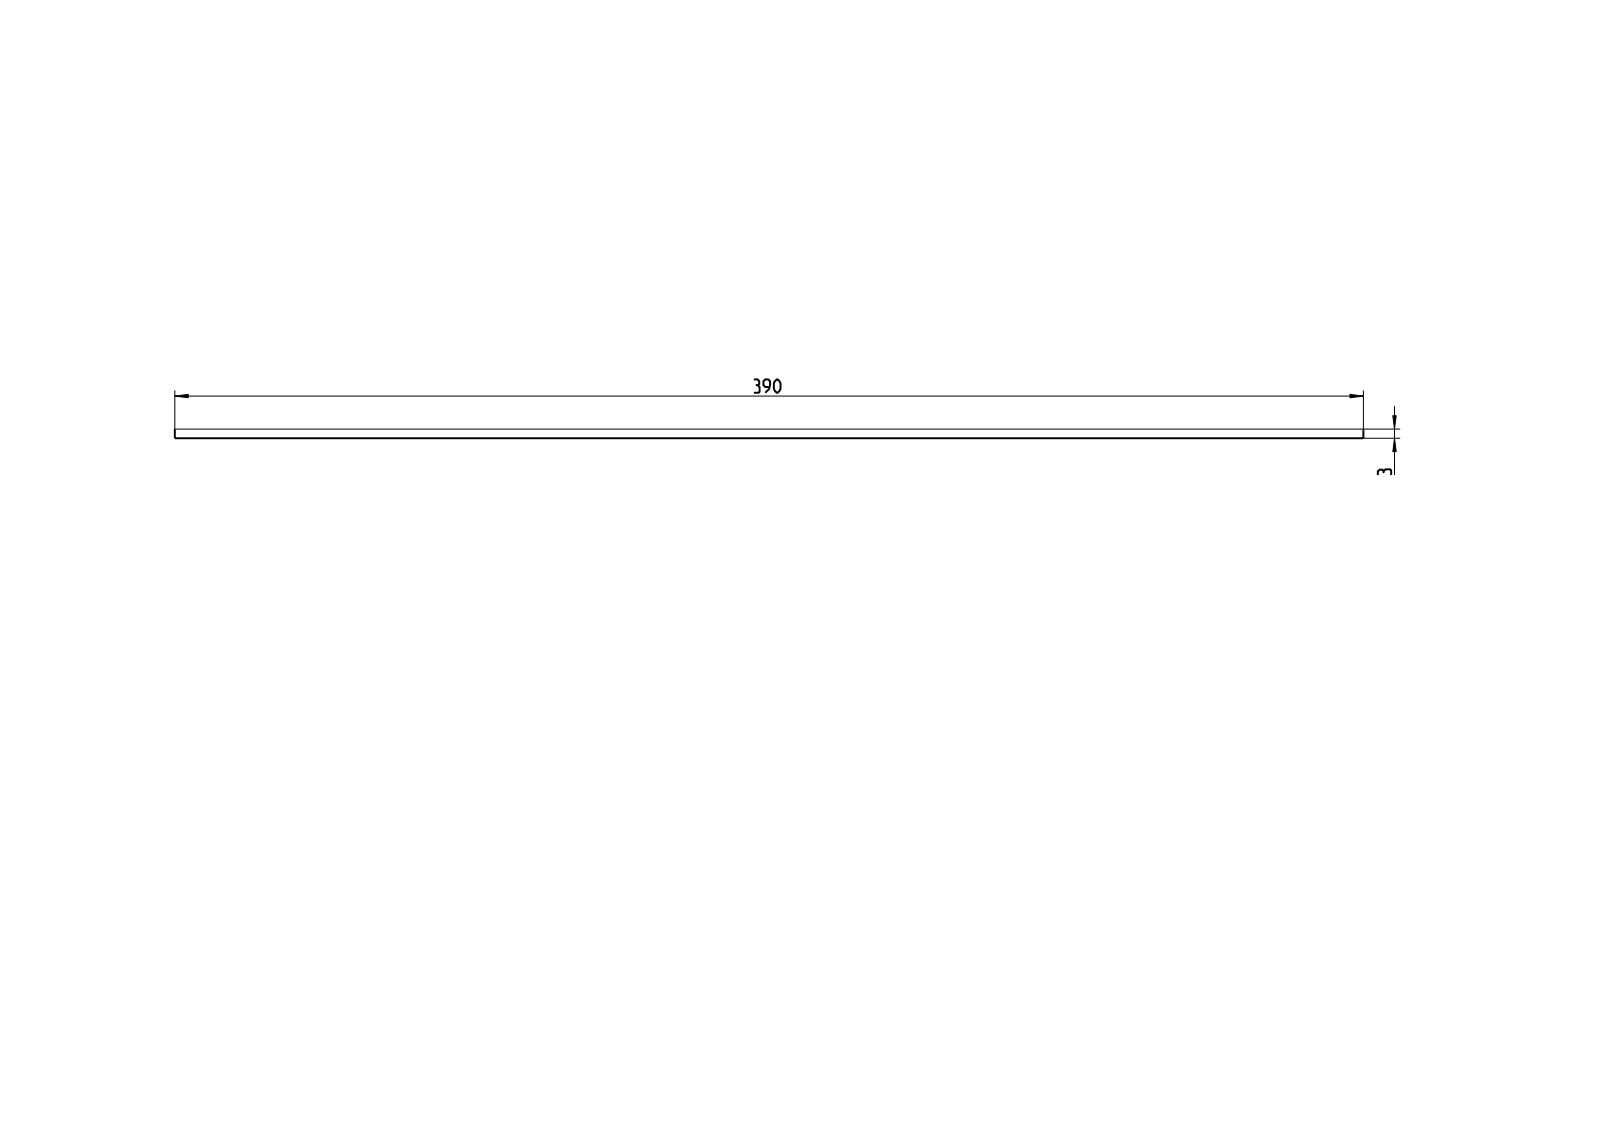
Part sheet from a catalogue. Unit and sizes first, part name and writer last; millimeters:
Units: millimetres
Overall size (bounding box): 999 × 390 × 3
Main face-to-face distances: 3, 390, 999
Volume: 1 169 000 mm³ · Surface area: 787 554 mm²
Bodies: 1 solid, 6 faces (6 planar, 0 cylindrical, 0 other)
Part name (STEP PRODUCT): T-01187; BKG4002BL2_ASM
STEP written by: CREO PARAMETRIC BY PTC INC, 2022024 (AUTOMOTIVE_DESIGN)
